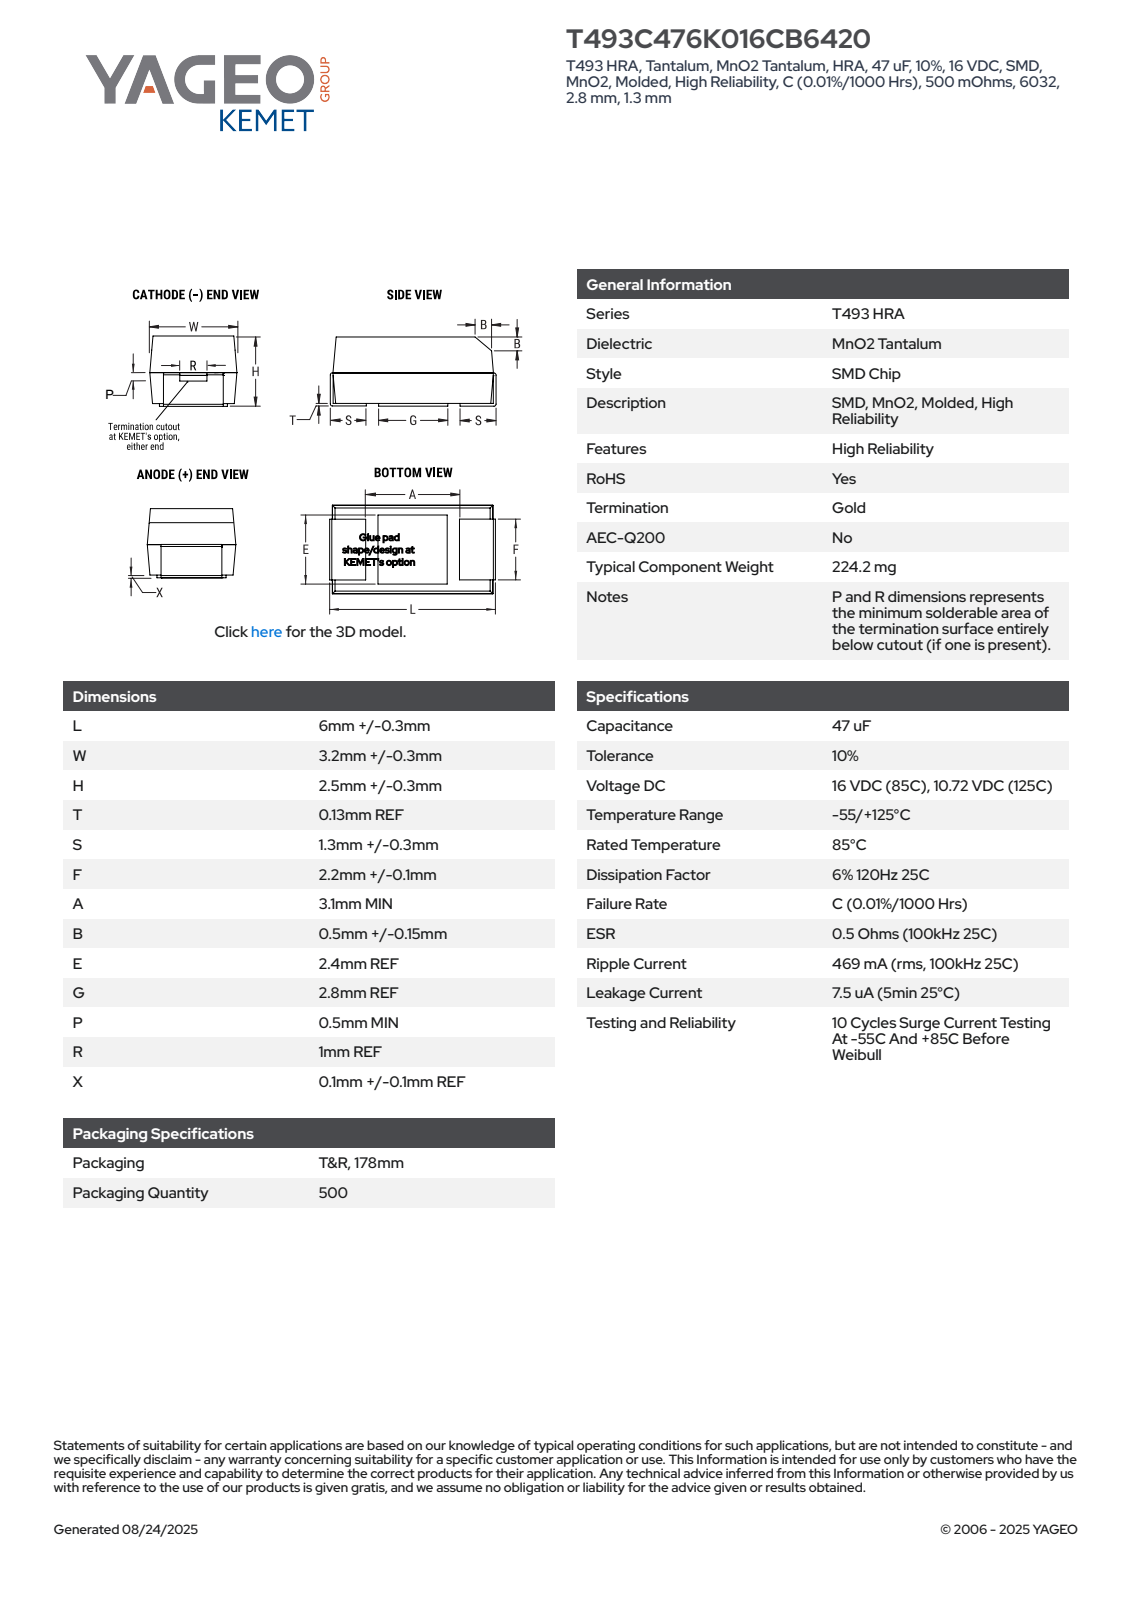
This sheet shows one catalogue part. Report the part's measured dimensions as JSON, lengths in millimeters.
{"part_name": "CTSM_TCM2NK_6032_L6.3W3.5H2.8T0.13S1.3F2.3A3.1B0.65E2.4G2.8P0.5R1X0.2", "step_written_by": "SolidWorks 2020 (AUTOMOTIVE_DESIGN)", "units": "millimeters", "bodies": {"solids": 4, "faces": 100, "planar": 95, "cylindrical": 5, "other": 0}, "overall_size": [6.3, 3.5, 2.81], "volume_mm3": 53, "surface_area_mm2": 108, "partial_cylinders_radius": [[0.1, 4]], "face_to_face_distances": [2.8, 2.6, 3.46, 3.47, 2.67, 6.17, 6.3, 6.04, 1.75, 4.55]}
